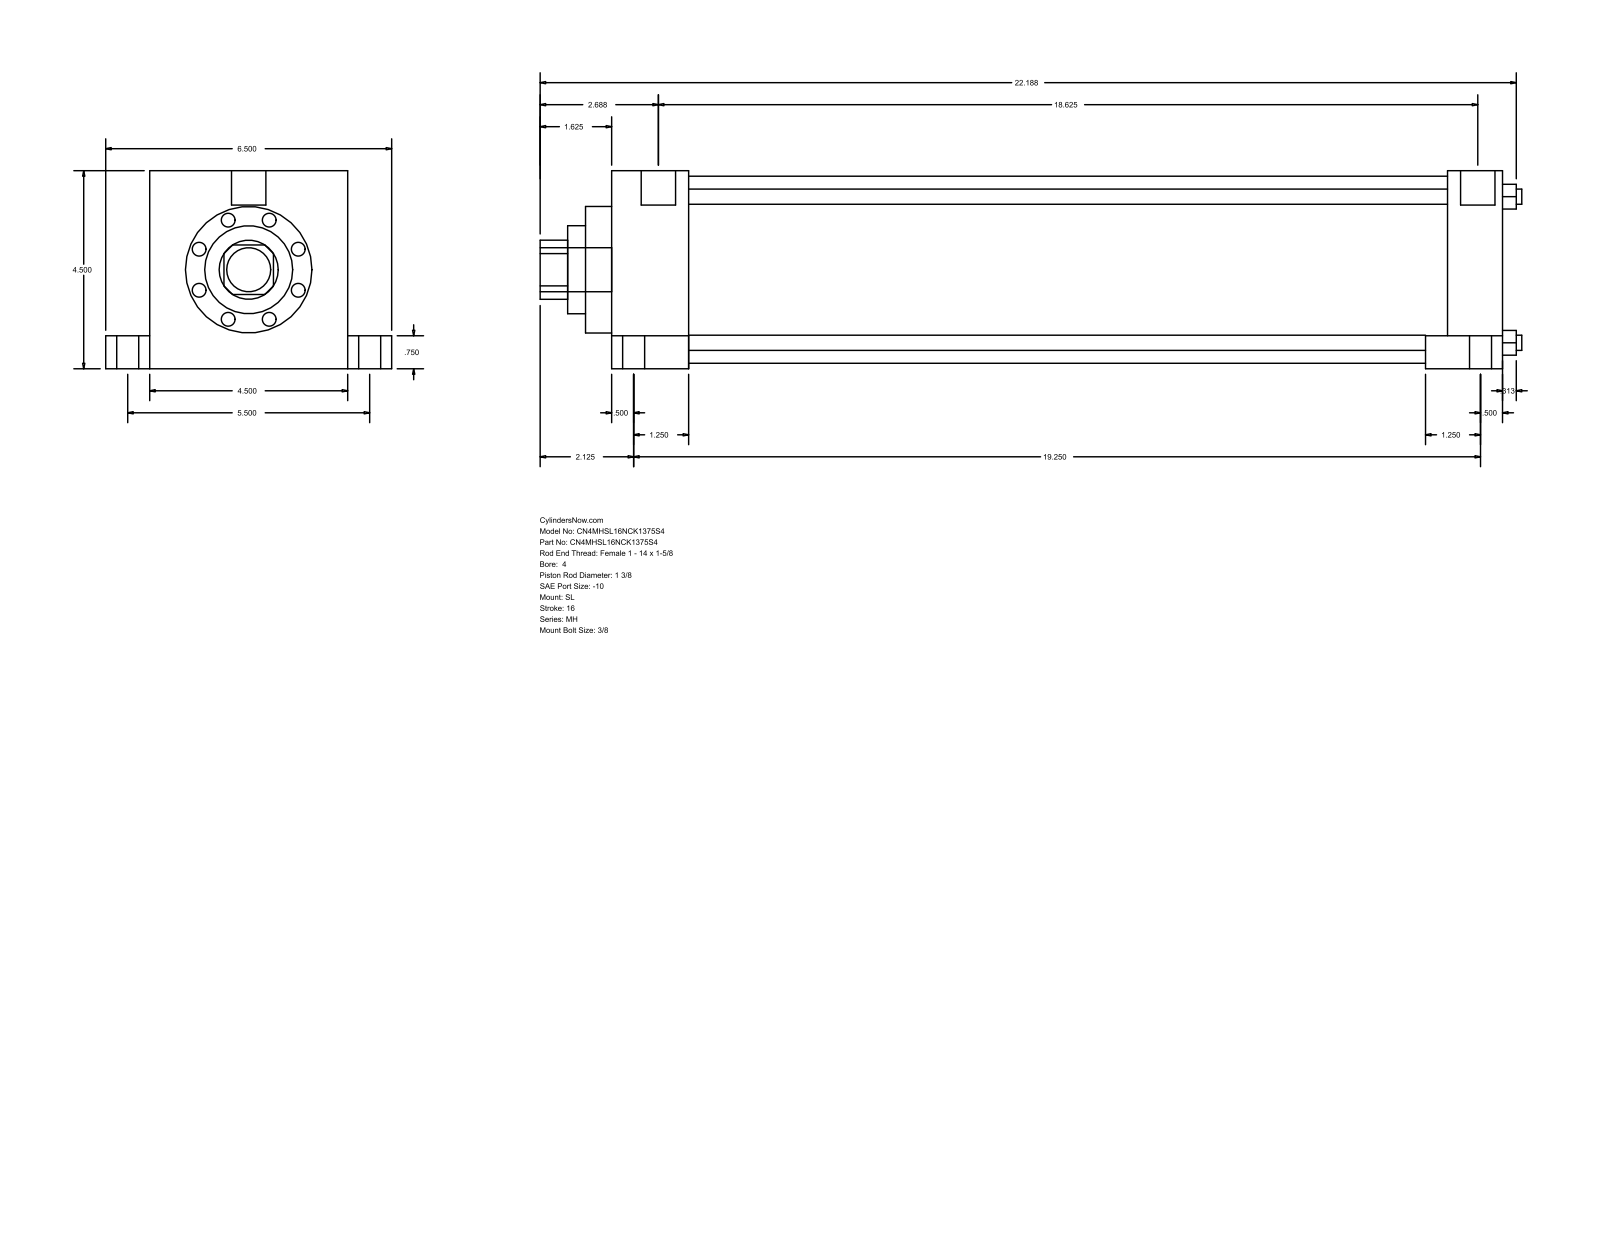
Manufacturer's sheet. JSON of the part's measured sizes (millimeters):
{"part_name": "MH_SL__0400_1.375", "step_written_by": "GSSL Pune (CONFIG_CONTROL_DESIGN)", "units": "millimeters", "bodies": {"solids": 0, "faces": 110, "planar": 77, "cylindrical": 33, "other": 0}, "overall_size": [566.74, 165.1, 114.3], "round_holes": [[8.76, 4], [34.92, 1], [50.8, 1], [73.03, 1], [107.95, 1]], "round_bosses_or_shafts": [[19.05, 4], [12.7, 4], [8.73, 4], [19.84, 2], [25.4, 1]], "partial_cylinders_radius": [[17.06, 1]], "face_to_face_distances": [114.3, 514.35, 44.45, 469.9, 482.61, 438.16, 31.74, 25.4, 139.7, 19.05], "hole_center_spacings": [59.62, 84.32, 119.25]}
